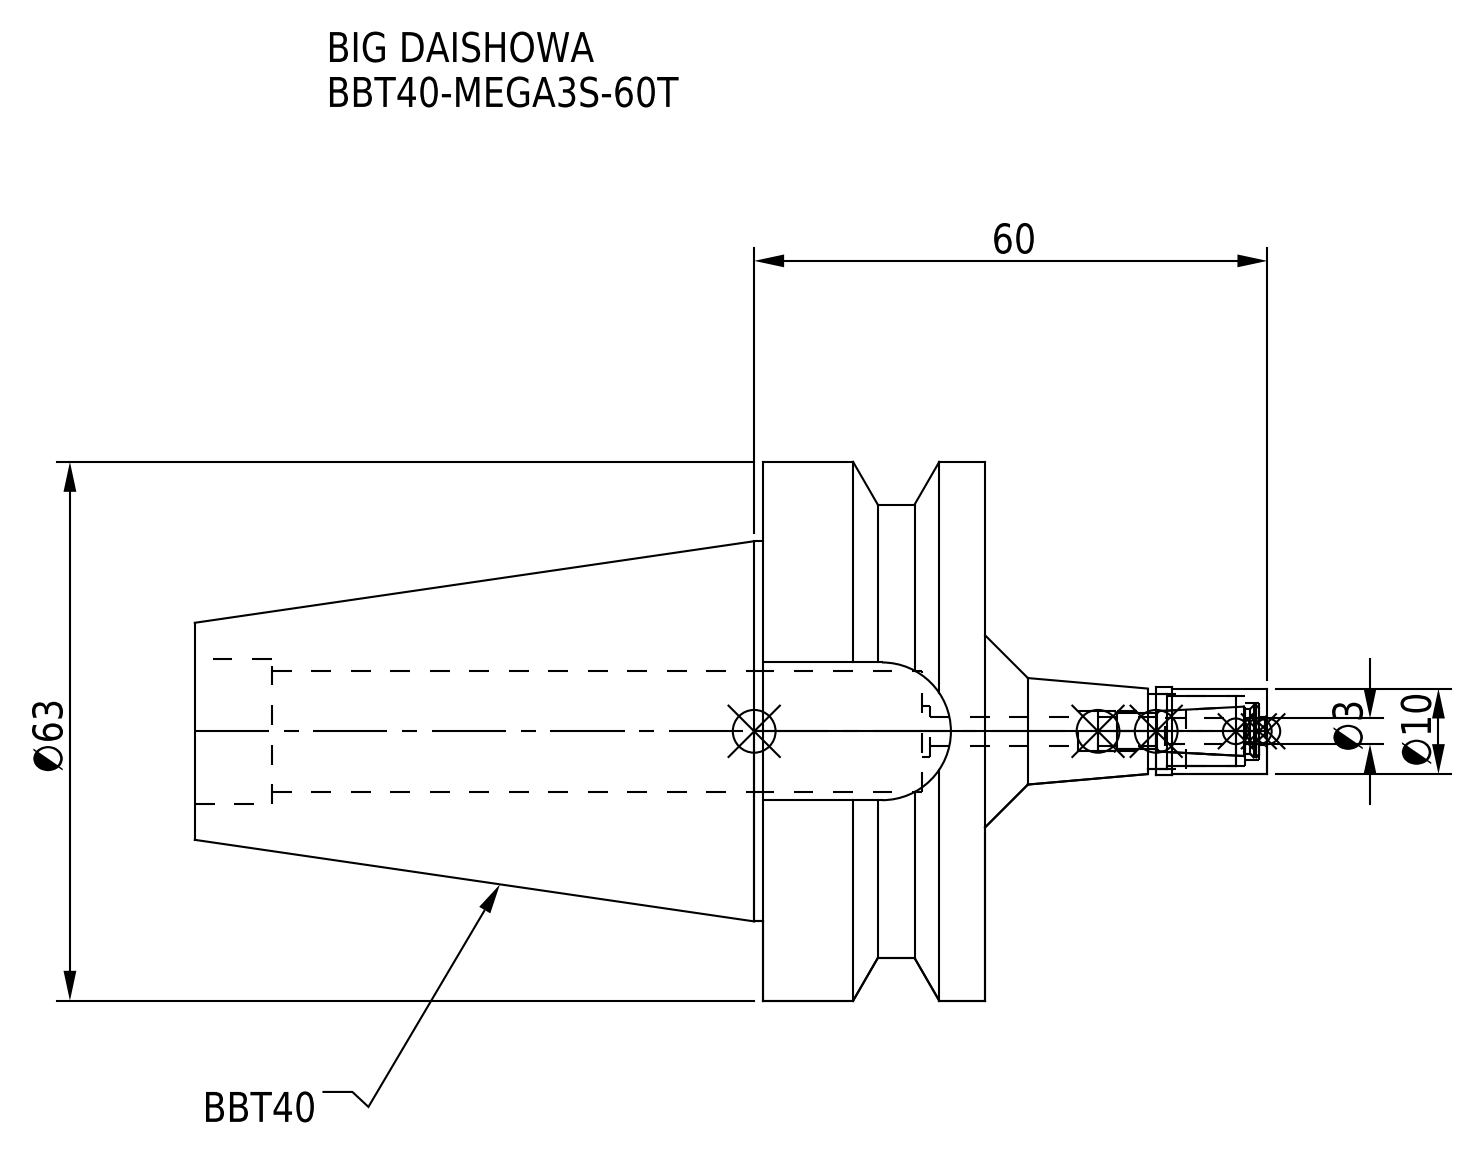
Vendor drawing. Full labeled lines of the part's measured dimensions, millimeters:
Part name (STEP PRODUCT): DXF_TEMP_ASSY_ASM_4_ASM.stp; BBT40-MEGA3S-60T_1.stp; BBT40-MEGA3S-60T-030-FreeParts; BBT40-MEGA3S-60T-030.stp (+3 more)
STEP written by: SolidWorks 2019 (CONFIG_CONTROL_DESIGN)
Units: millimetres
Bodies: 2 solids, 74 faces (22 planar, 38 cylindrical, 14 other)
Overall size (bounding box): 125.4 × 63 × 63
Volume: 124 532 mm³ · Surface area: 24 857 mm²
Round holes (diameter × count): ⌀3.3 ×1, ⌀3.4 ×1, ⌀4.7 ×1, ⌀6 ×1, ⌀6.6 ×1, ⌀8.2 ×1, ⌀8.7 ×1, ⌀14.2 ×1, ⌀17 ×1
Round bosses / shafts (diameter × count): ⌀63 ×1, ⌀53 ×1, ⌀44.45 ×1, ⌀10.3 ×1, ⌀10 ×1
Partial cylindrical surfaces — rounded edges, fillets, slot ends (radius × count): R8.05 ×1
Main face-to-face distances: 26, 45, 92.4, 66.4, 16.1, 7.4, 18.6, 85, 83.4, 76
